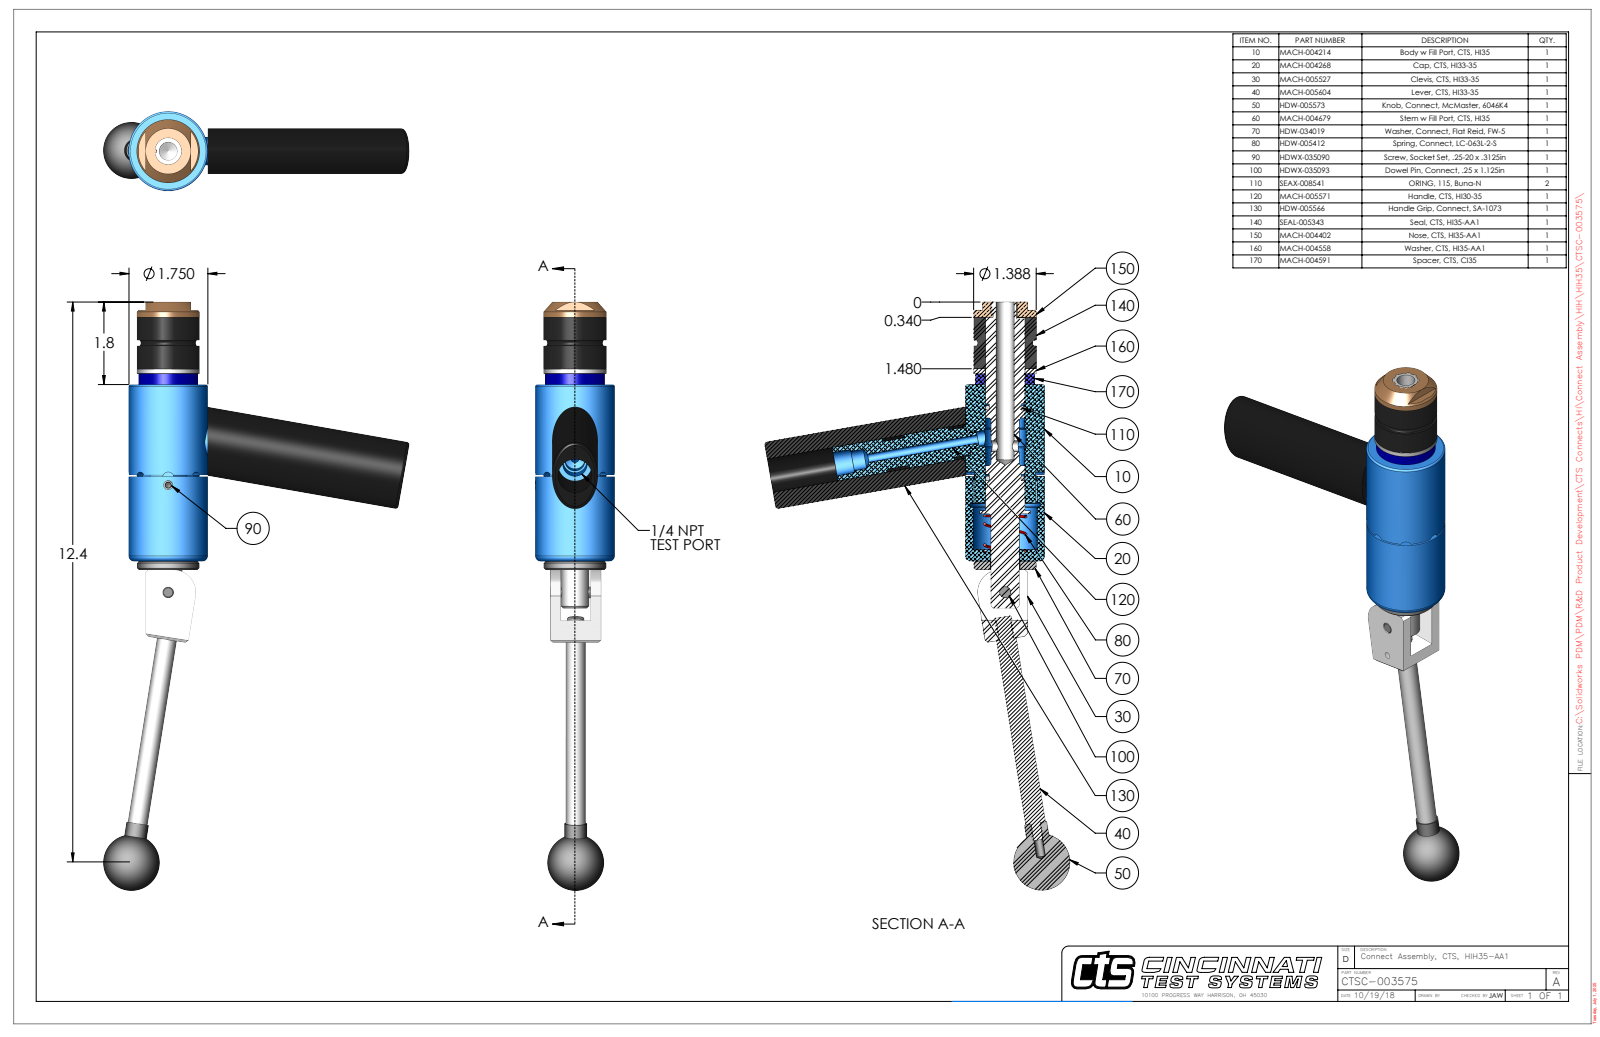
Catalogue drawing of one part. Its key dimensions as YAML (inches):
part_name: "CTSC-003575"
step_written_by: "SolidWorks 2023 (AUTOMOTIVE_DESIGN)"
units: inches
bodies: {solids: 12, faces: 306, planar: 112, cylindrical: 124, other: 70}
overall_size: [13.042, 6.763, 1.75]
volume: 19
surface_area: 127
round_holes:
  - {diameter: 0.201, count: 2}
  - {diameter: 0.15, count: 1}
  - {diameter: 0.187, count: 1}
  - {diameter: 0.249, count: 1}
  - {diameter: 0.25, count: 1}
  - {diameter: 0.251, count: 1}
  - {diameter: 0.313, count: 1}
  - {diameter: 0.406, count: 1}
  - {diameter: 0.438, count: 1}
  - {diameter: 0.531, count: 1}
  - {diameter: 0.635, count: 1}
  - {diameter: 0.656, count: 1}
round_bosses_or_shafts:
  - {diameter: 0.25, count: 2}
  - {diameter: 1.75, count: 1}
  - {diameter: 1.388, count: 1}
  - {diameter: 1.38, count: 1}
  - {diameter: 1.312, count: 1}
  - {diameter: 0.869, count: 1}
  - {diameter: 0.75, count: 1}
  - {diameter: 0.625, count: 1}
partial_cylinders:
  - {radius: 0.125, count: 4}
  - {radius: 0.029, count: 2}
  - {radius: 0.249, count: 1}
  - {radius: 0.33, count: 1}
  - {radius: 0.5, count: 1}
  - {radius: 0.695, count: 1}
  - {radius: 0.831, count: 1}
face_to_face_distances: [3.915, 1.49, 5.405, 1.14, 0.35, 4.265, 1.25, 0.11, 0.24, 4.155]
hole_center_spacings: [0.74, 2.376, 3.116]
